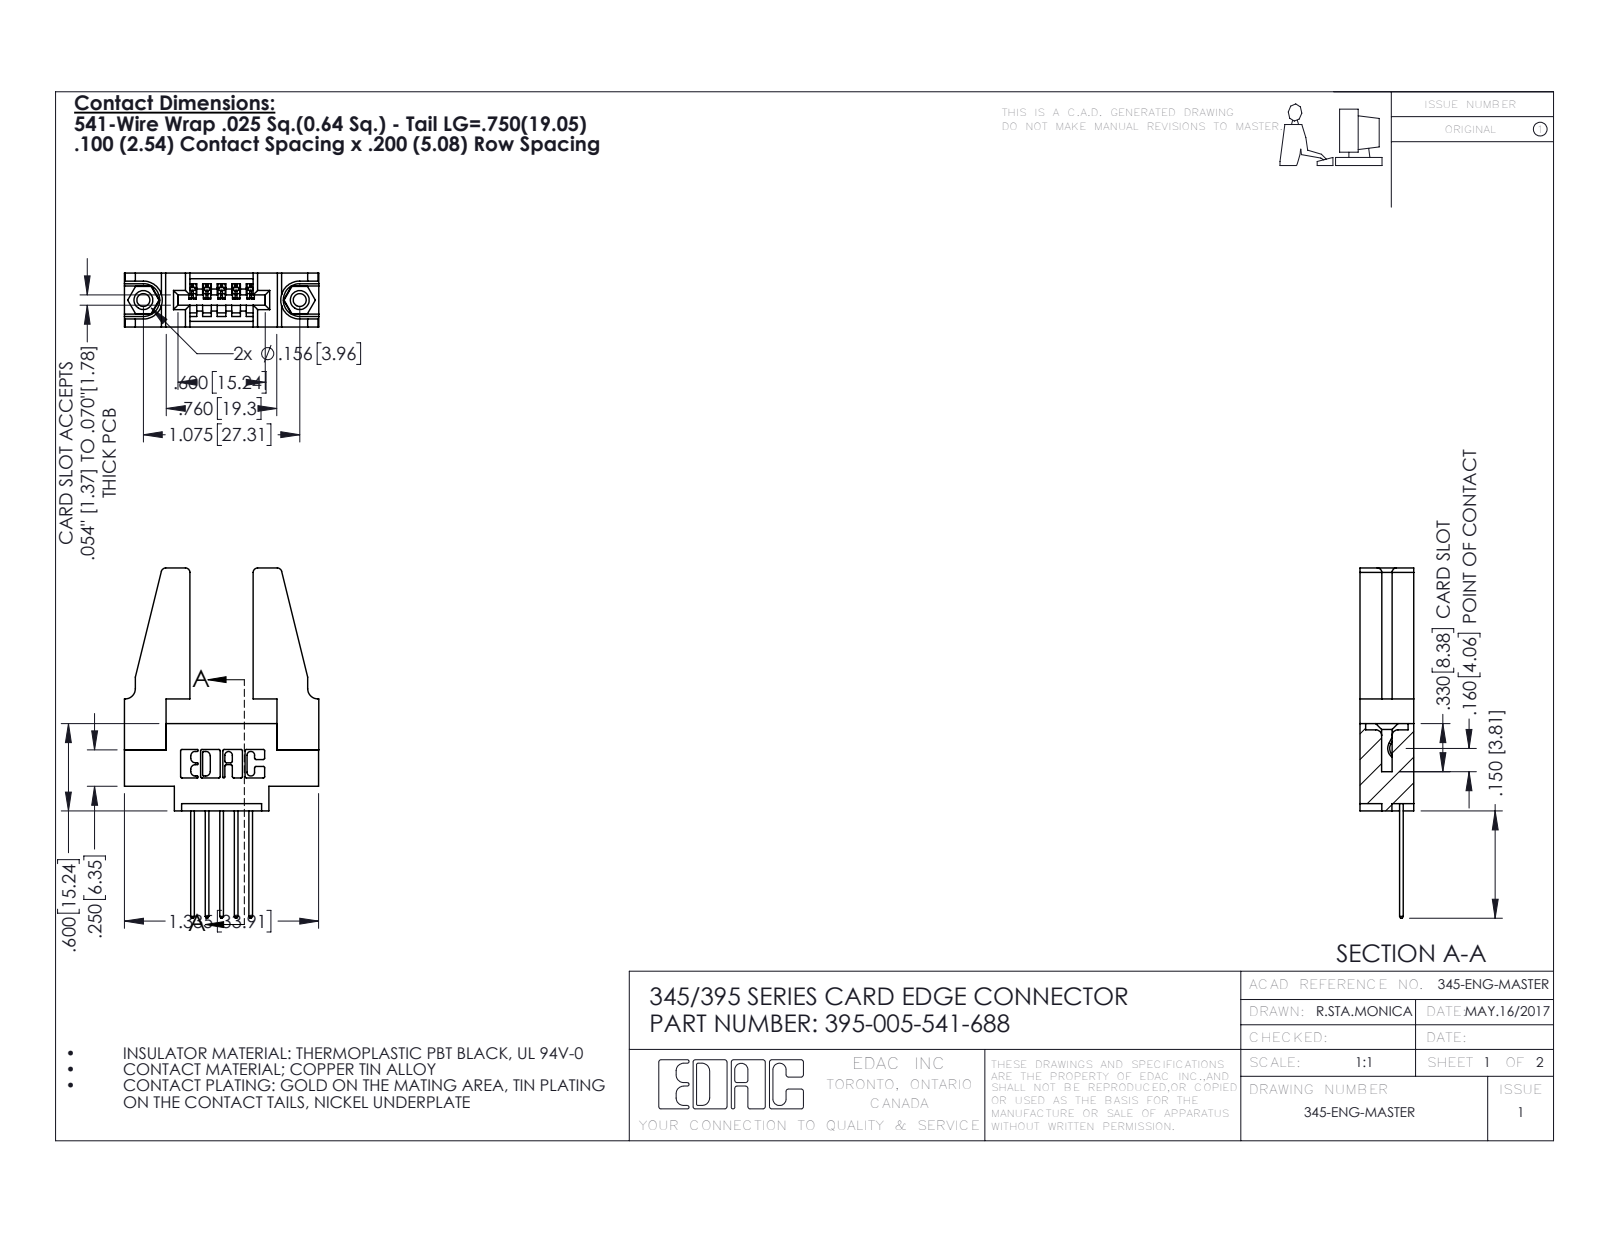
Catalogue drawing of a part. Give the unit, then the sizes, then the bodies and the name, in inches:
Units: inches
Overall size (bounding box): 2.407 × 1.336 × 0.37
Round holes (diameter × count): ⌀0.089 ×2, ⌀0.125 ×2, ⌀0.156 ×2, ⌀0.064 ×1
Round bosses / shafts (diameter × count): ⌀0.155 ×2
Partial cylindrical surfaces — rounded edges, fillets, slot ends (radius × count): R0.01 ×22, R0.006 ×10, R0.01 ×10, R0.03 ×8, R0.007 ×6, R0.031 ×6, R0.026 ×3, R0.031 ×2
Main face-to-face distances: 0.37, 0.072, 0.298, 0.2, 0.148, 0.15, 0.098, 0.272, 0.025, 0.22
Hole centre spacings: 0.27, 0.847, 1.075
Volume: 0.371 in³ · Surface area: 10.23 in²
Bodies: 10 solids, 544 faces (356 planar, 172 cylindrical, 16 other)
Part name (STEP PRODUCT): 345-220-078_345-220-088; 345 Part_0.170 Offset - 0.156 Dia-TH; 395-005-541-688; 345-292-001_345-293-141 (+1 more)
STEP written by: SolidWorks 2016 (CONFIG_CONTROL_DESIGN)
